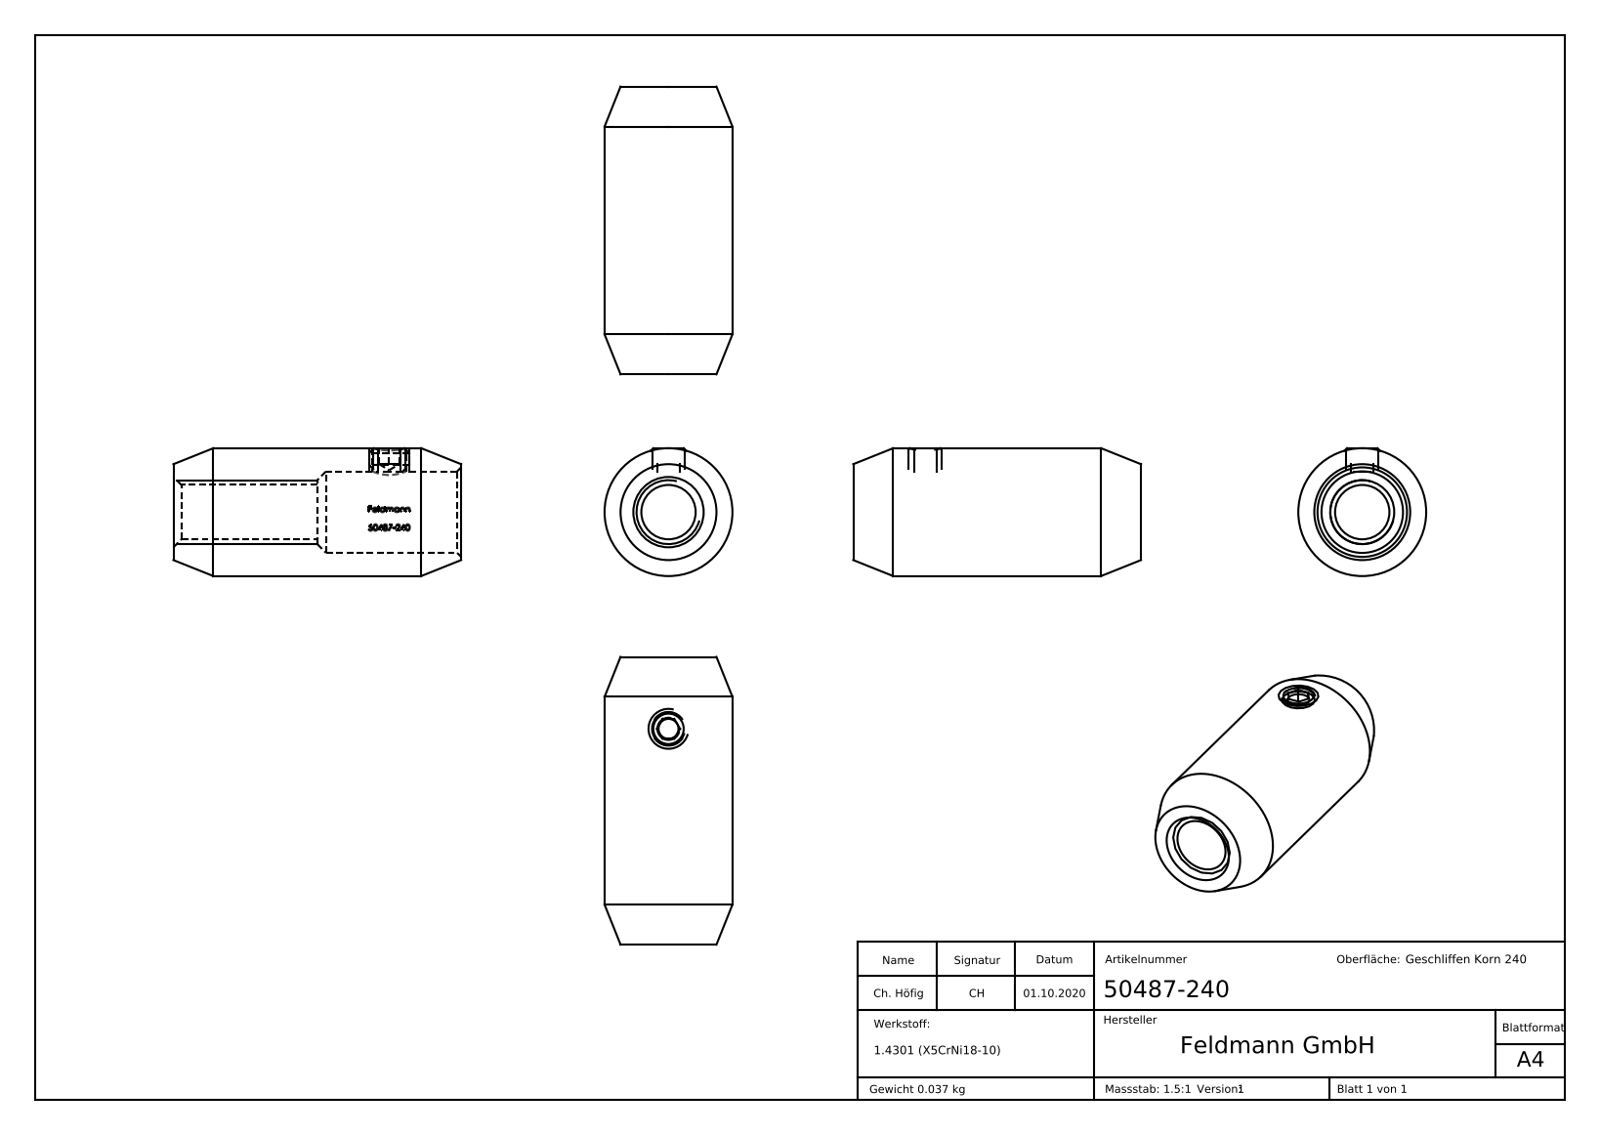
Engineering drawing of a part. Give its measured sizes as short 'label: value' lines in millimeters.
name: DIN913_DIN 913 M5x3; 50487-240; DIN913; 5048X-240 Teil1_50487-240 Teil1 (+1 more)
written by: SolidWorks 2018 (CONFIG_CONTROL_DESIGN)
unit: mm
bodies: 2 solids, 268 faces (119 planar, 36 cylindrical, 113 other)
size: 70 × 36 × 16
volume: 4 653 mm³; area: 2 960 mm²
holes: 1× ⌀4.2, 1× ⌀6.8, 1× ⌀10.2
bosses: 1× ⌀16, 1× ⌀5
rounds: 1× R5.2
face distances: 18, 36, 2.5, 3, 7.75, 10.25, 28.25, 25.75, 2, 1
